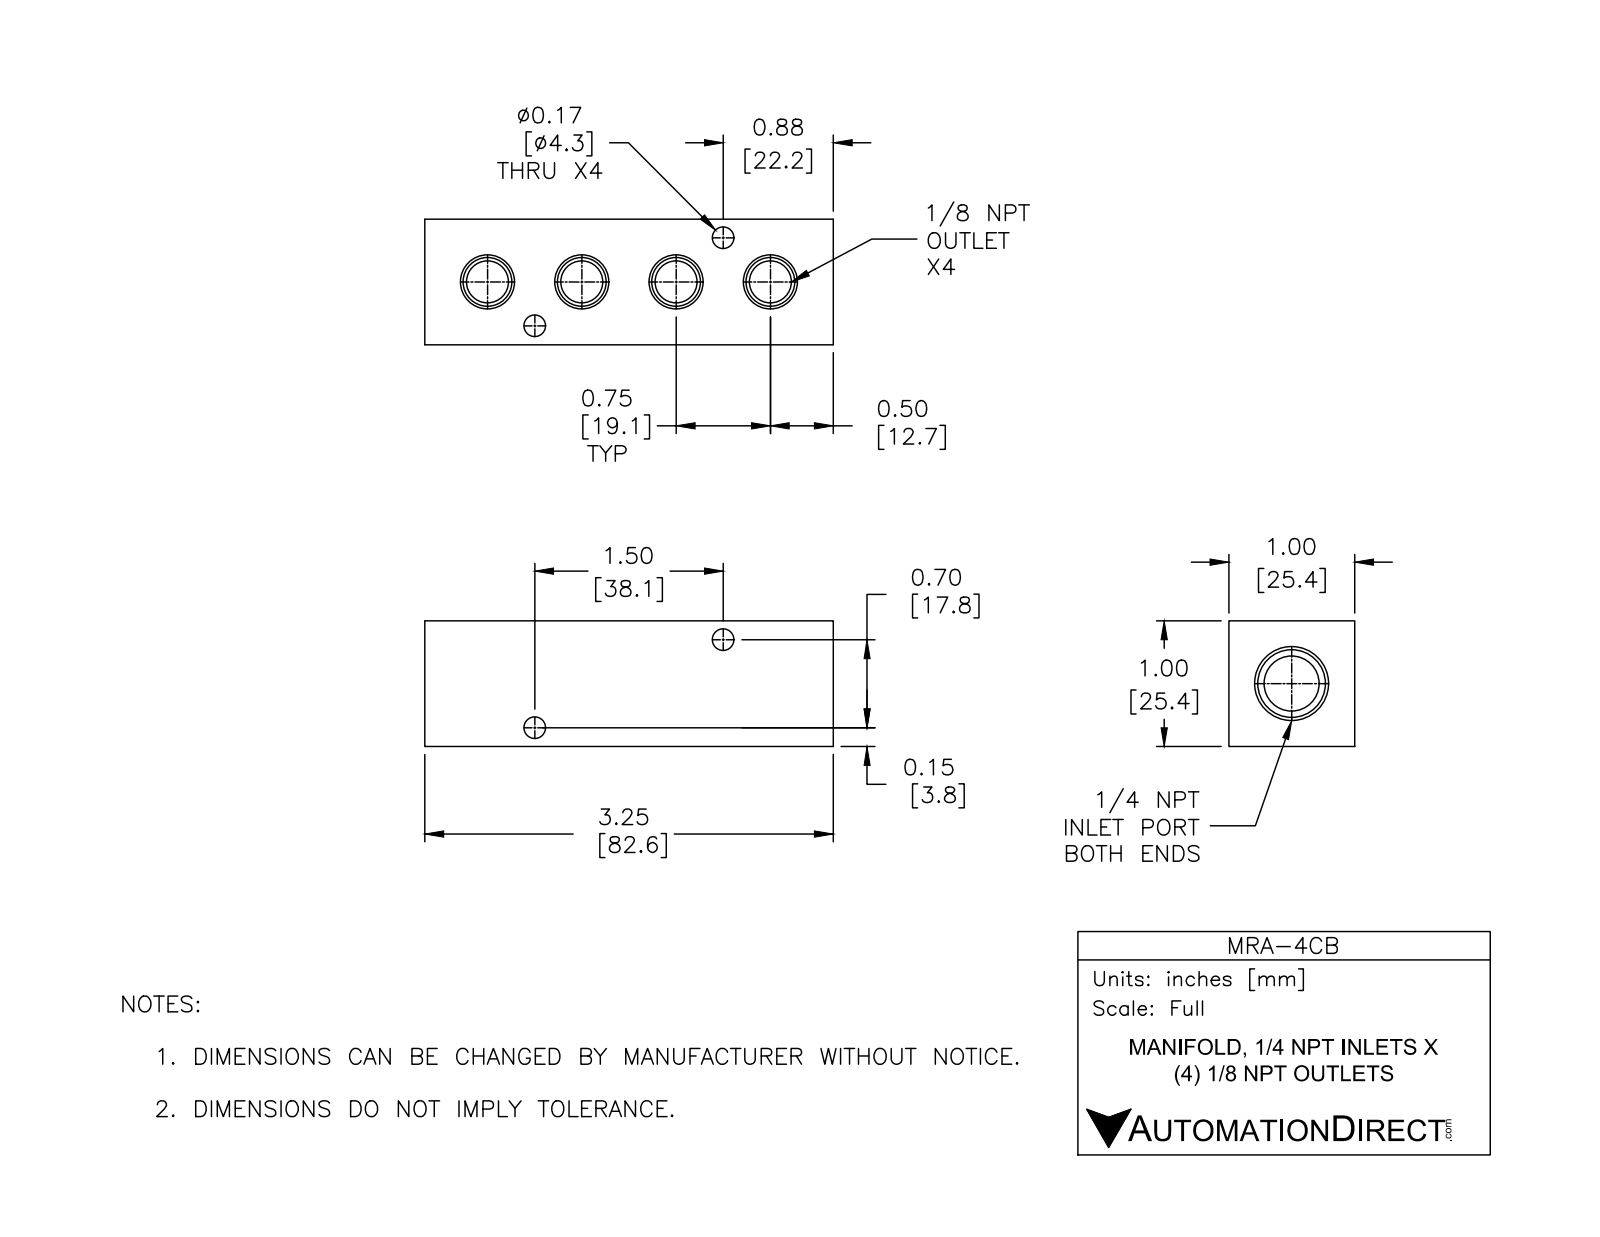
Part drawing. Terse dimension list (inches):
name: MRA-4CB
written by: SolidWorks 2015 (CONFIG_CONTROL_DESIGN)
unit: in
bodies: 1 solid, 61 faces (12 planar, 25 cylindrical, 24 other)
size: 3.25 × 1 × 1
volume: 2.478 in³; area: 21.7 in²
holes: 4× ⌀0.17, 2× ⌀0.332, 1× ⌀0.438
rounds: 2× R0.166
face distances: 1, 3.25, 0.73, 0.27, 0.39, 2.86, 2.47
hole spacings: 0.513, 1.655, 0.75, 1.178, 1.178
